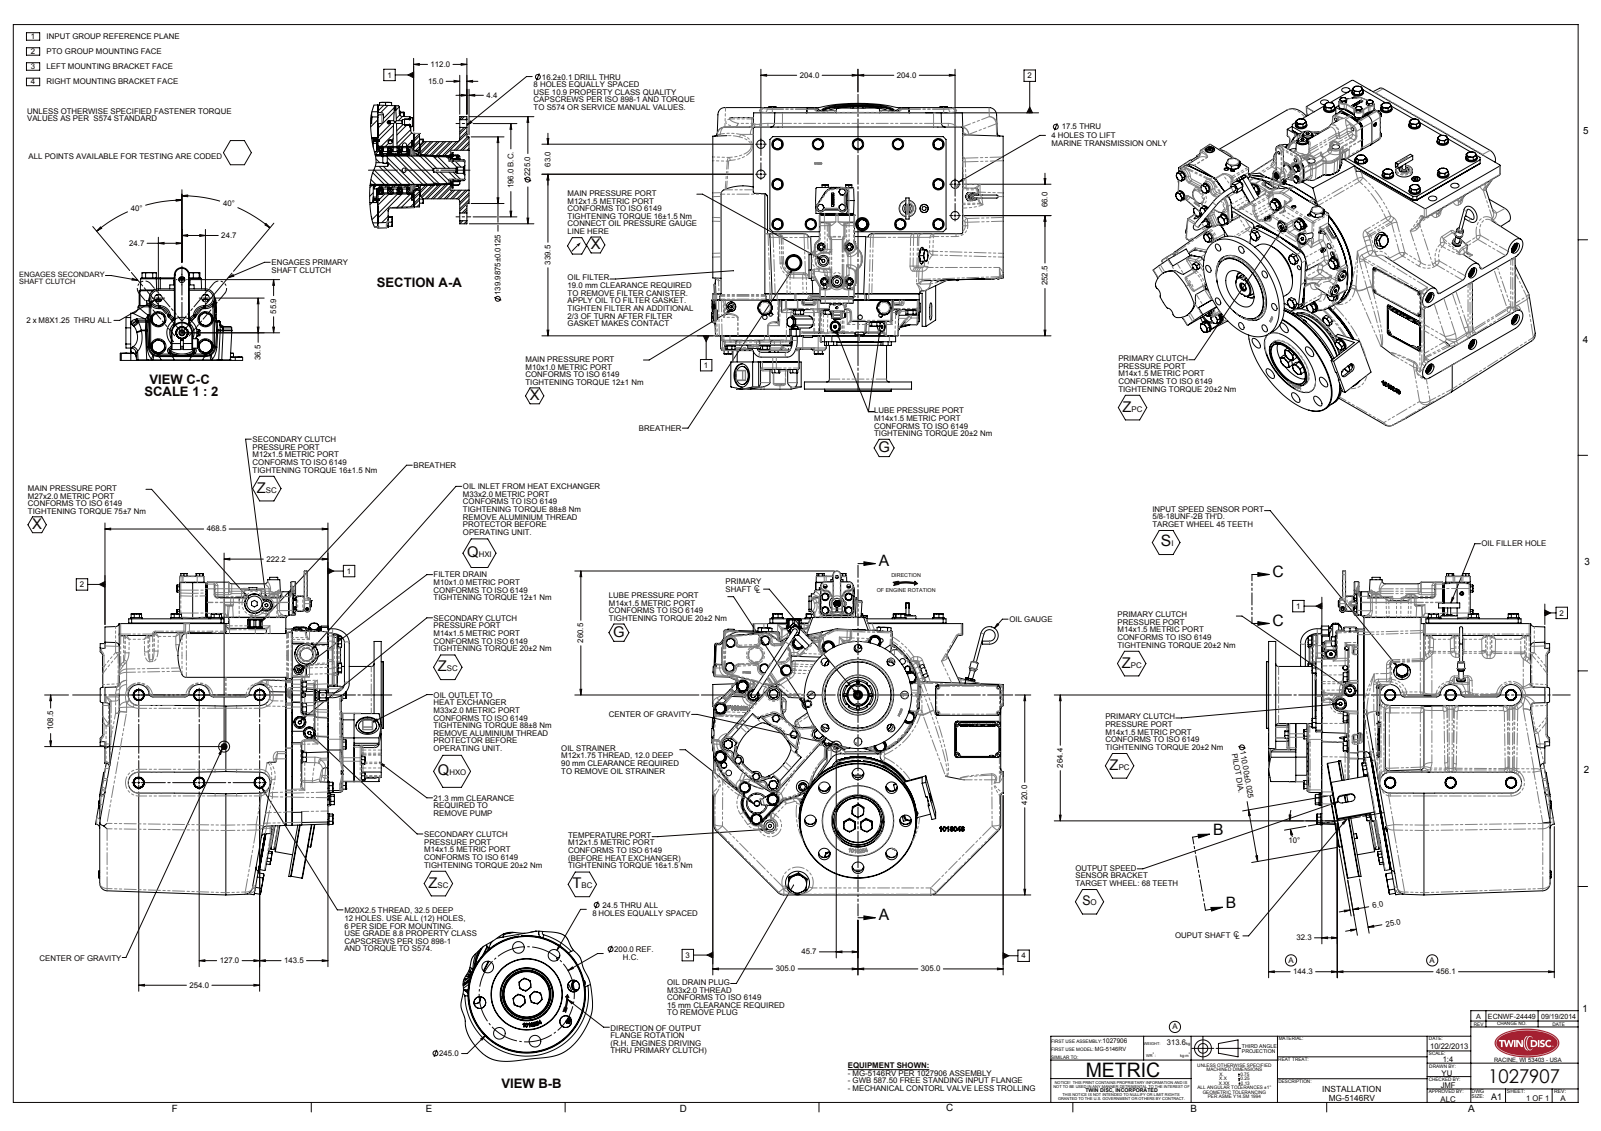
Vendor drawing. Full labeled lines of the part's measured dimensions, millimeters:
Part name (STEP PRODUCT): 1027907
STEP written by: SolidWorks 2010 (AUTOMOTIVE_DESIGN)
Units: millimetres
Bodies: 0 solids, 7735 faces (4424 planar, 1359 cylindrical, 1952 other)
Overall size (bounding box): 680.53 × 615.4 × 604.75
Round holes (diameter × count): ⌀12 ×18, ⌀16.2 ×8, ⌀24.5 ×8, ⌀25 ×8, ⌀8 ×7, ⌀23.51 ×6, ⌀20 ×5, ⌀6.4 ×4, ⌀7.71 ×4, ⌀9.5 ×4, ⌀14 ×4, ⌀16.5 ×4
Round bosses / shafts (diameter × count): ⌀24 ×27, ⌀19 ×8, ⌀19.85 ×5, ⌀10 ×5, ⌀17 ×4, ⌀14 ×4, ⌀6.35 ×4, ⌀13 ×3
Partial cylindrical surfaces — rounded edges, fillets, slot ends (radius × count): R3 ×106, R8 ×74, R6.5 ×62, R2.5 ×57, R16 ×32, R1.52 ×27, R6.4 ×26, R1.5 ×22
Main face-to-face distances: 0.39, 13.09, 404.48, 404.09, 13.48, 391, 89.27, 75, 75.39, 88.48
Hole centre spacings: 100, 76.54, 82, 141.42, 184.77, 184.78, 127, 200
